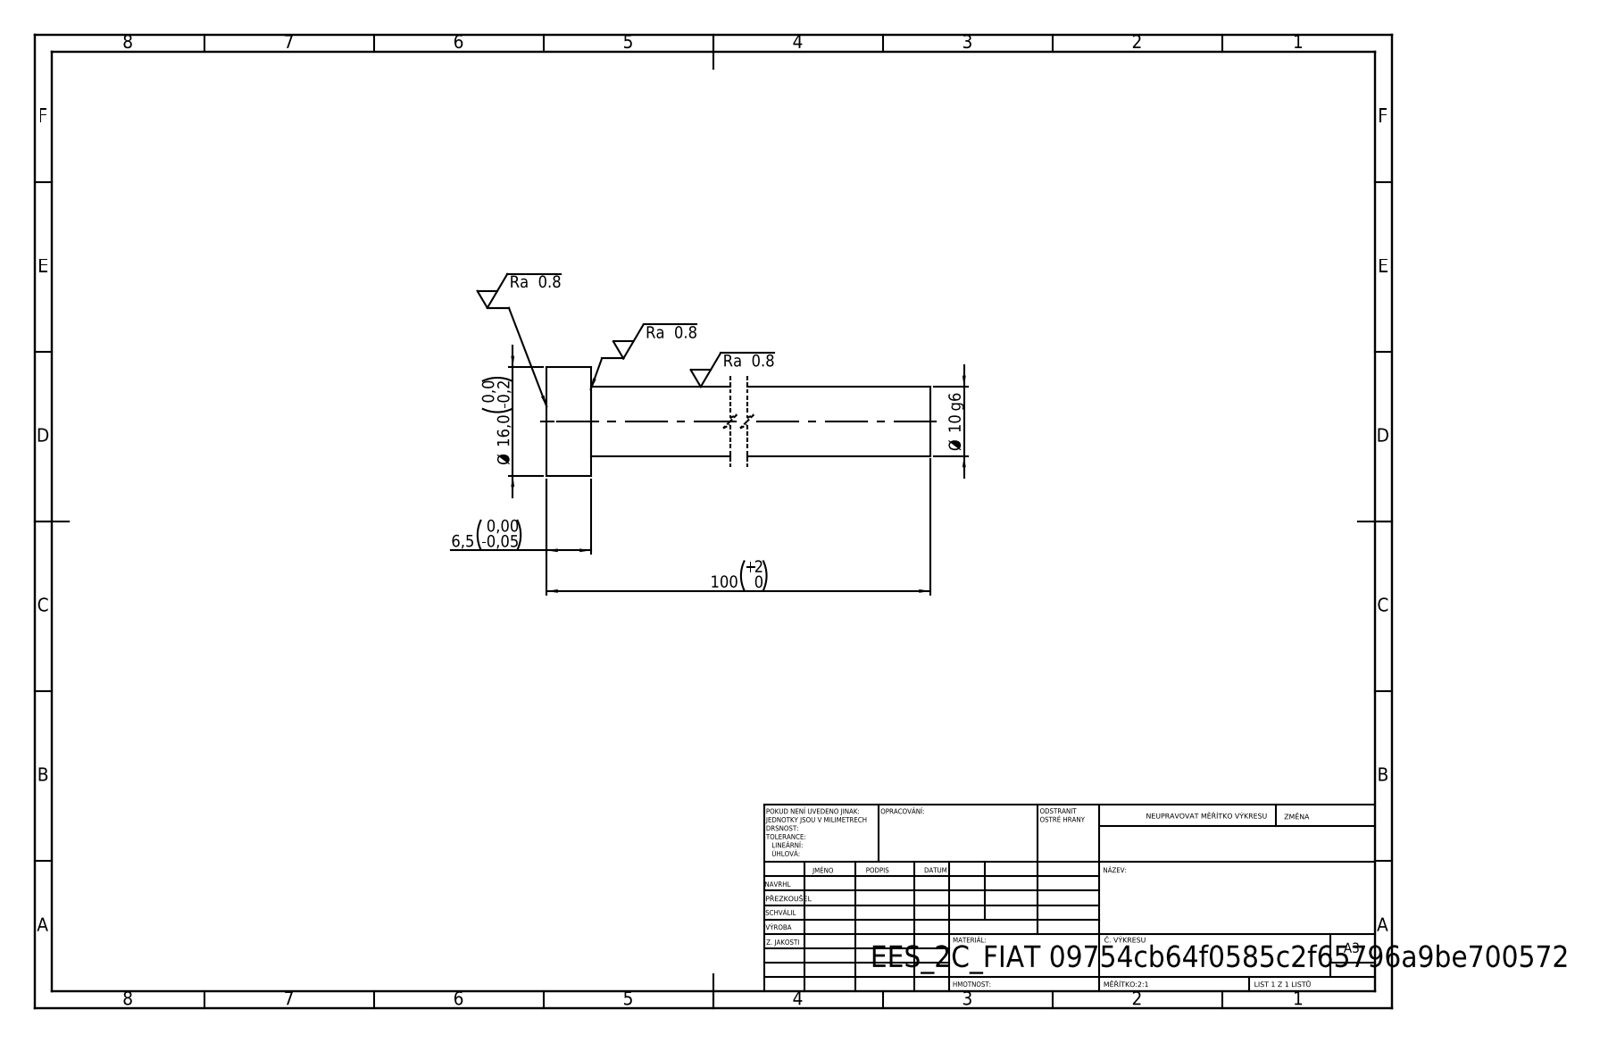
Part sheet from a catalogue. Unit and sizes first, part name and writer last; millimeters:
Units: millimetres
Overall size (bounding box): 100 × 16 × 16
Round bosses / shafts (diameter × count): ⌀16 ×1, ⌀10.2 ×1
Main face-to-face distances: 6.5, 100, 93.5
Volume: 8 947 mm³ · Surface area: 3 725 mm²
Bodies: 1 solid, 7 faces (3 planar, 4 cylindrical, 0 other)
STEP written by: SolidWorks 2019 (CONFIG_CONTROL_DESIGN)
